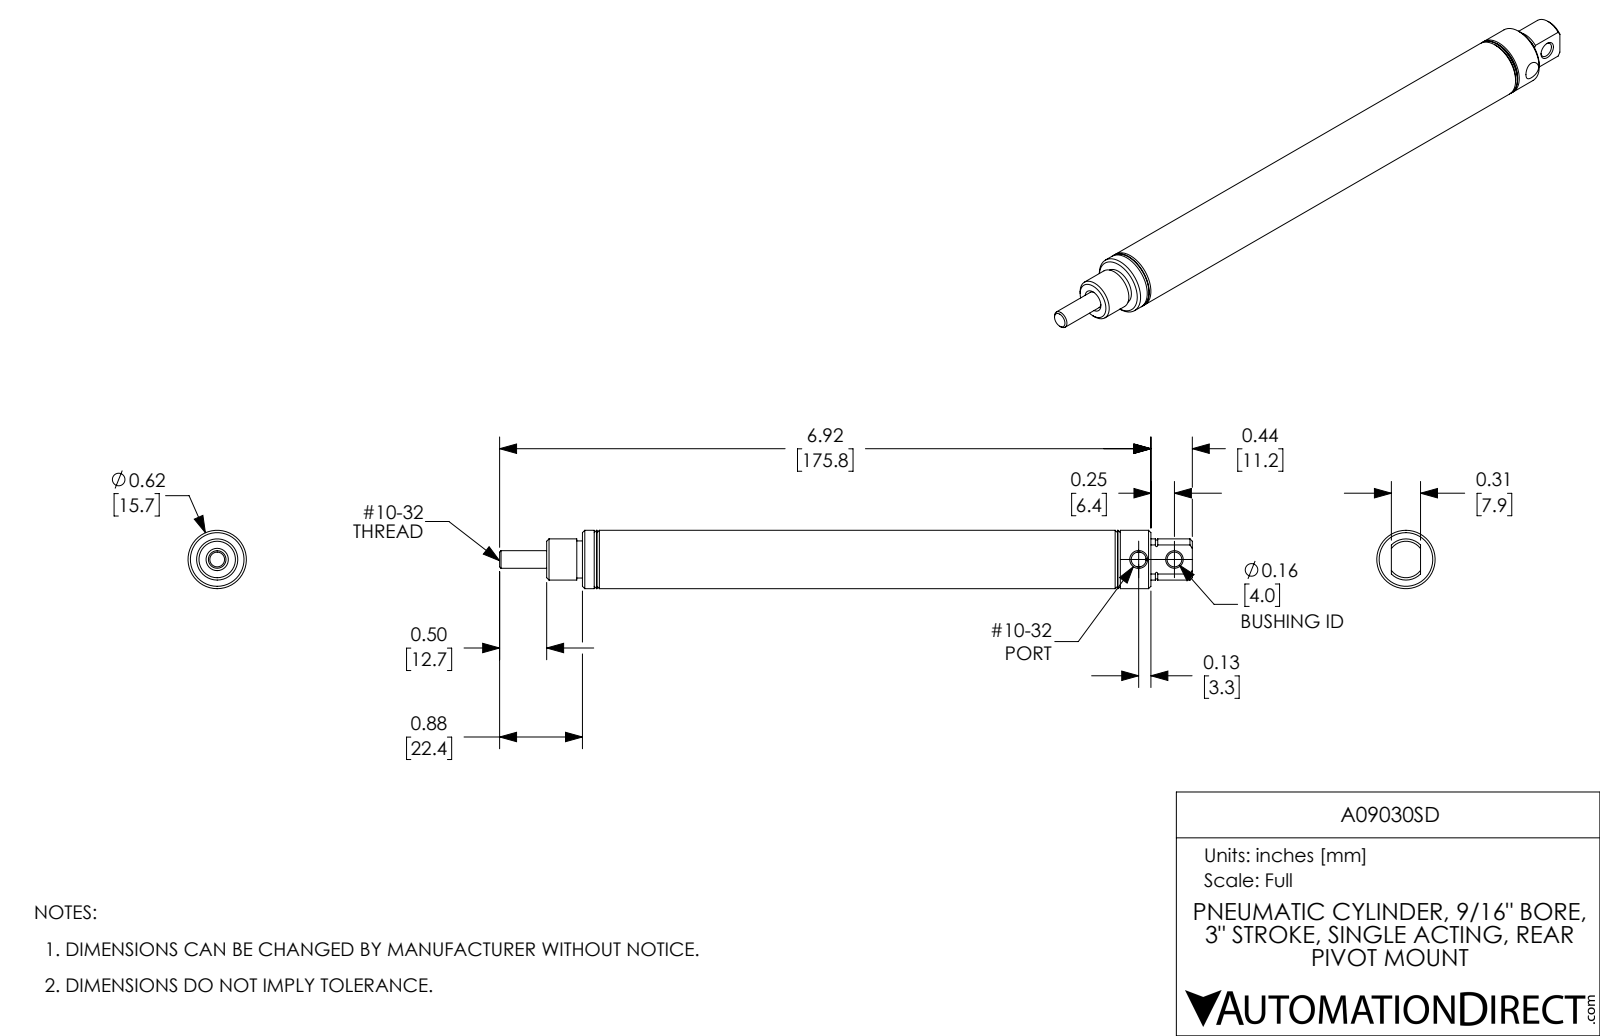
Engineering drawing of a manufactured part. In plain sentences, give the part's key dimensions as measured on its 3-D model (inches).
The part is named "A09030SD; A09030SD-Rod; A09030SD-MainBody". Its 3-D file was written by "SolidWorks 2017 (AUTOMOTIVE_DESIGN)". It is 2 solids with 94 faces: 19 planar, 38 cylindrical and 37 other. Overall it measures 7.36 by 0.62 by 0.62 inches. Its volume is 1.243 cubic inches and its surface area 26.45 square inches. Round holes: 1 of diameter 0.156, 1 of diameter 0.157, 1 of diameter 0.159, 1 of diameter 0.187, 1 of diameter 0.19, 1 of diameter 0.563. Round bosses or shafts: 1 of diameter 0.62, 1 of diameter 0.437, 1 of diameter 0.394. The main face-to-face distances are 1.27, 4.77, 3.5, 0.5, 3, 4.27, 1.77, 6.04, 0.31, 0.44. The hole center spacings are 0.38.
